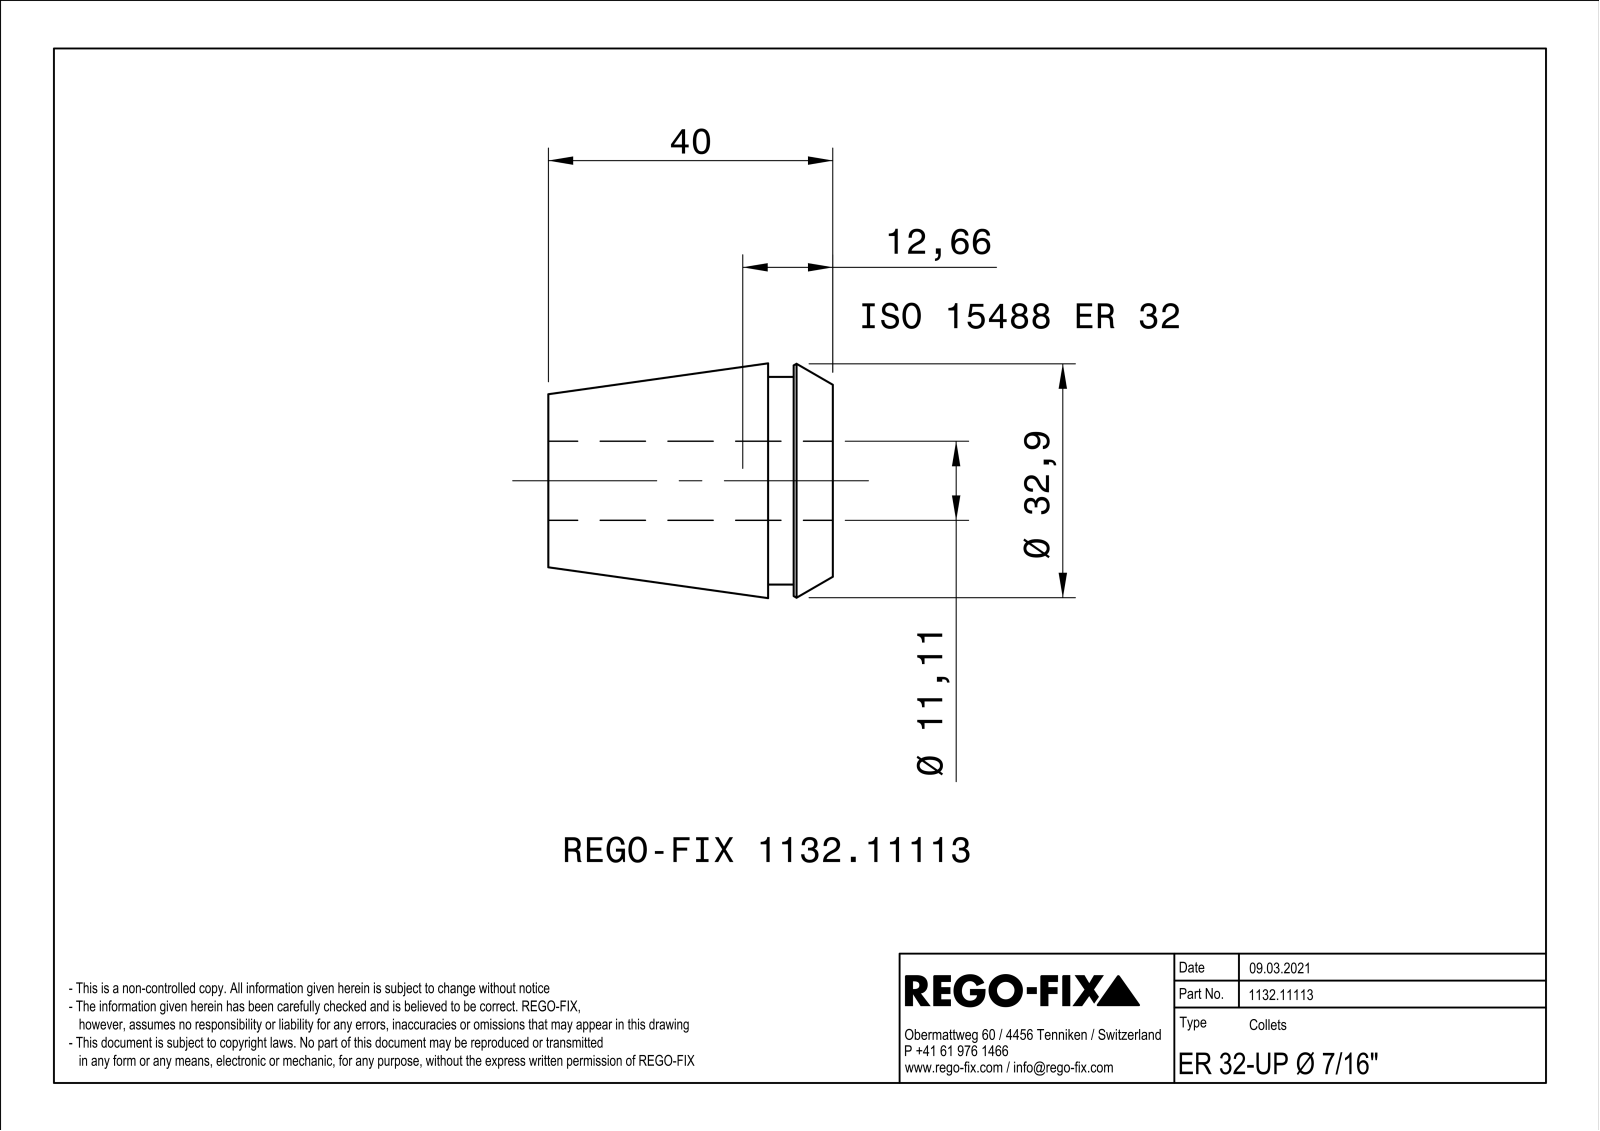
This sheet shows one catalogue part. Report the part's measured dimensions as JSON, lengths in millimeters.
{"part_name": "NOCUT", "step_written_by": "SIEMENS PLM Software Solid Edge ST10 (AUTOMOTIVE_DESIGN)", "units": "millimeters", "bodies": {"solids": 1, "faces": 209, "planar": 88, "cylindrical": 41, "other": 80}, "overall_size": [40, 32.98, 32.98], "volume_mm3": 17480, "surface_area_mm2": 15243, "round_holes": [[11.11, 1]], "round_bosses_or_shafts": [[29.2, 1]], "partial_cylinders_radius": [[0.4, 20]], "face_to_face_distances": [1, 40, 9.1, 30.9, 5.5, 3.6, 34.5, 6, 0.5, 3.1]}
